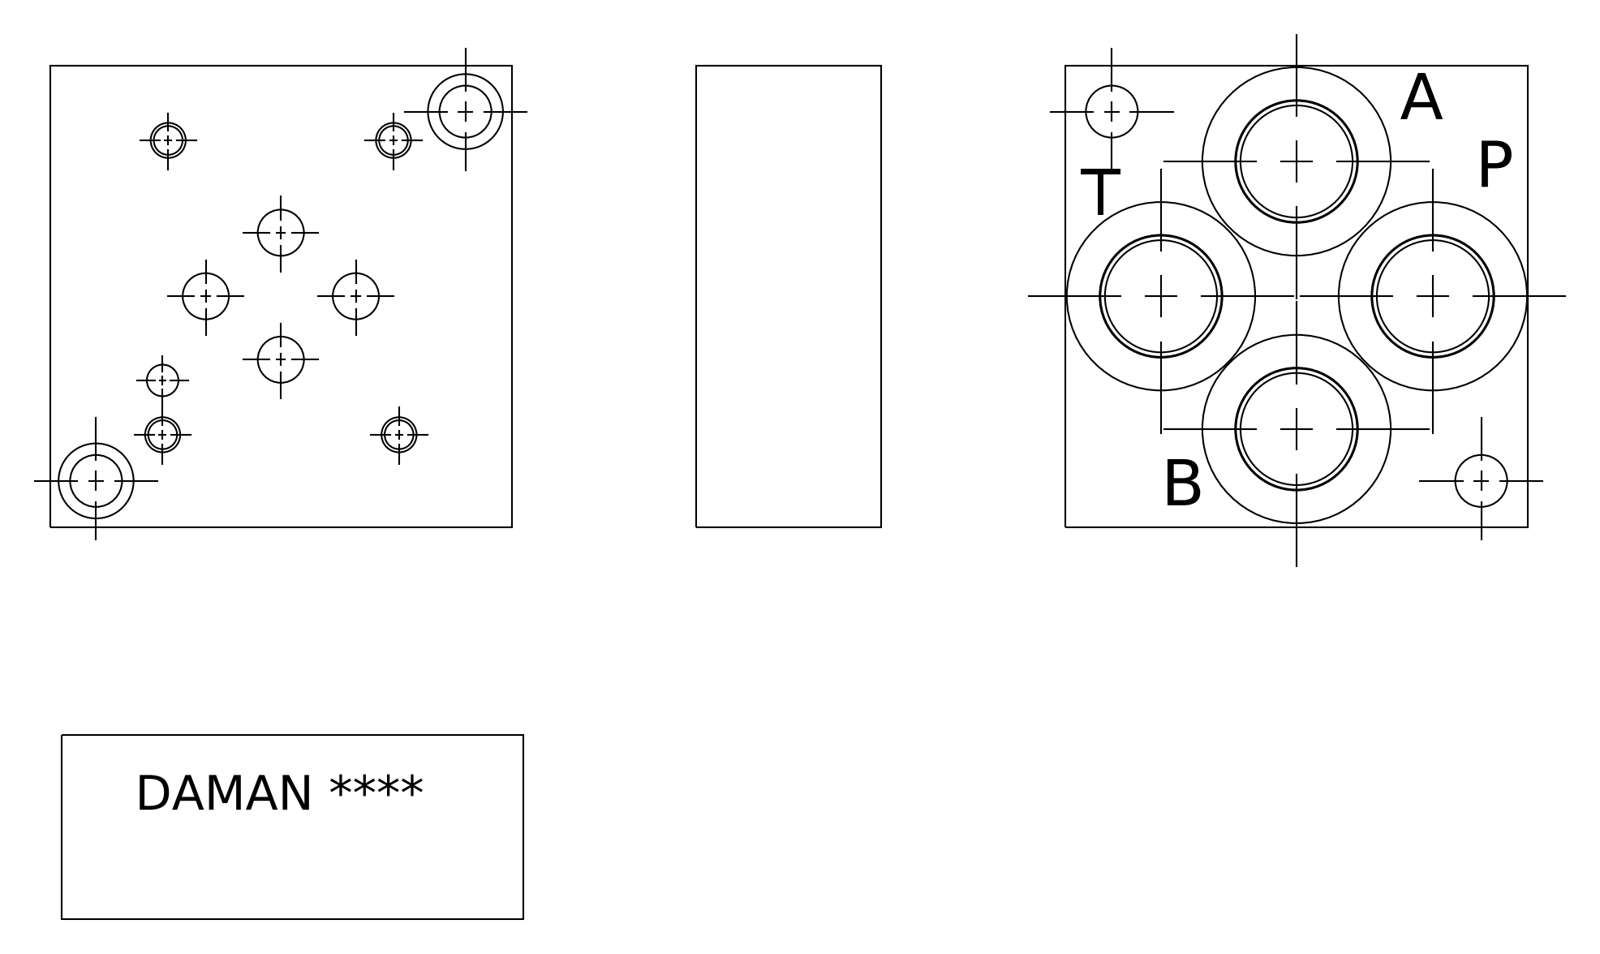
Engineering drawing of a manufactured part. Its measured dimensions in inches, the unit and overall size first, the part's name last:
Units: inches
Overall size (bounding box): 2.5 × 2.5 × 1
Round holes (diameter × count): ⌀0.281 ×6, ⌀0.166 ×4, ⌀0.197 ×4, ⌀0.562 ×4, ⌀0.593 ×4, ⌀0.66 ×4, ⌀1.021 ×4, ⌀0.406 ×2, ⌀0.156 ×1
Main face-to-face distances: 2.5, 1, 0.031, 0.969, 0.5, 0.511, 0.48, 0.489, 0.039, 2.461
Hole centre spacings: 0.532, 0.533, 0.811, 0.815, 0.868, 1.196, 1.321, 1.594
Volume: 4.813 in³ · Surface area: 34.24 in²
Bodies: 1 solid, 473 faces (283 planar, 33 cylindrical, 157 other)
Part name (STEP PRODUCT): Part_AD03SPB6B.B01911R3_3D
STEP written by: Autodesk Inventor 2019 (AUTOMOTIVE_DESIGN)
